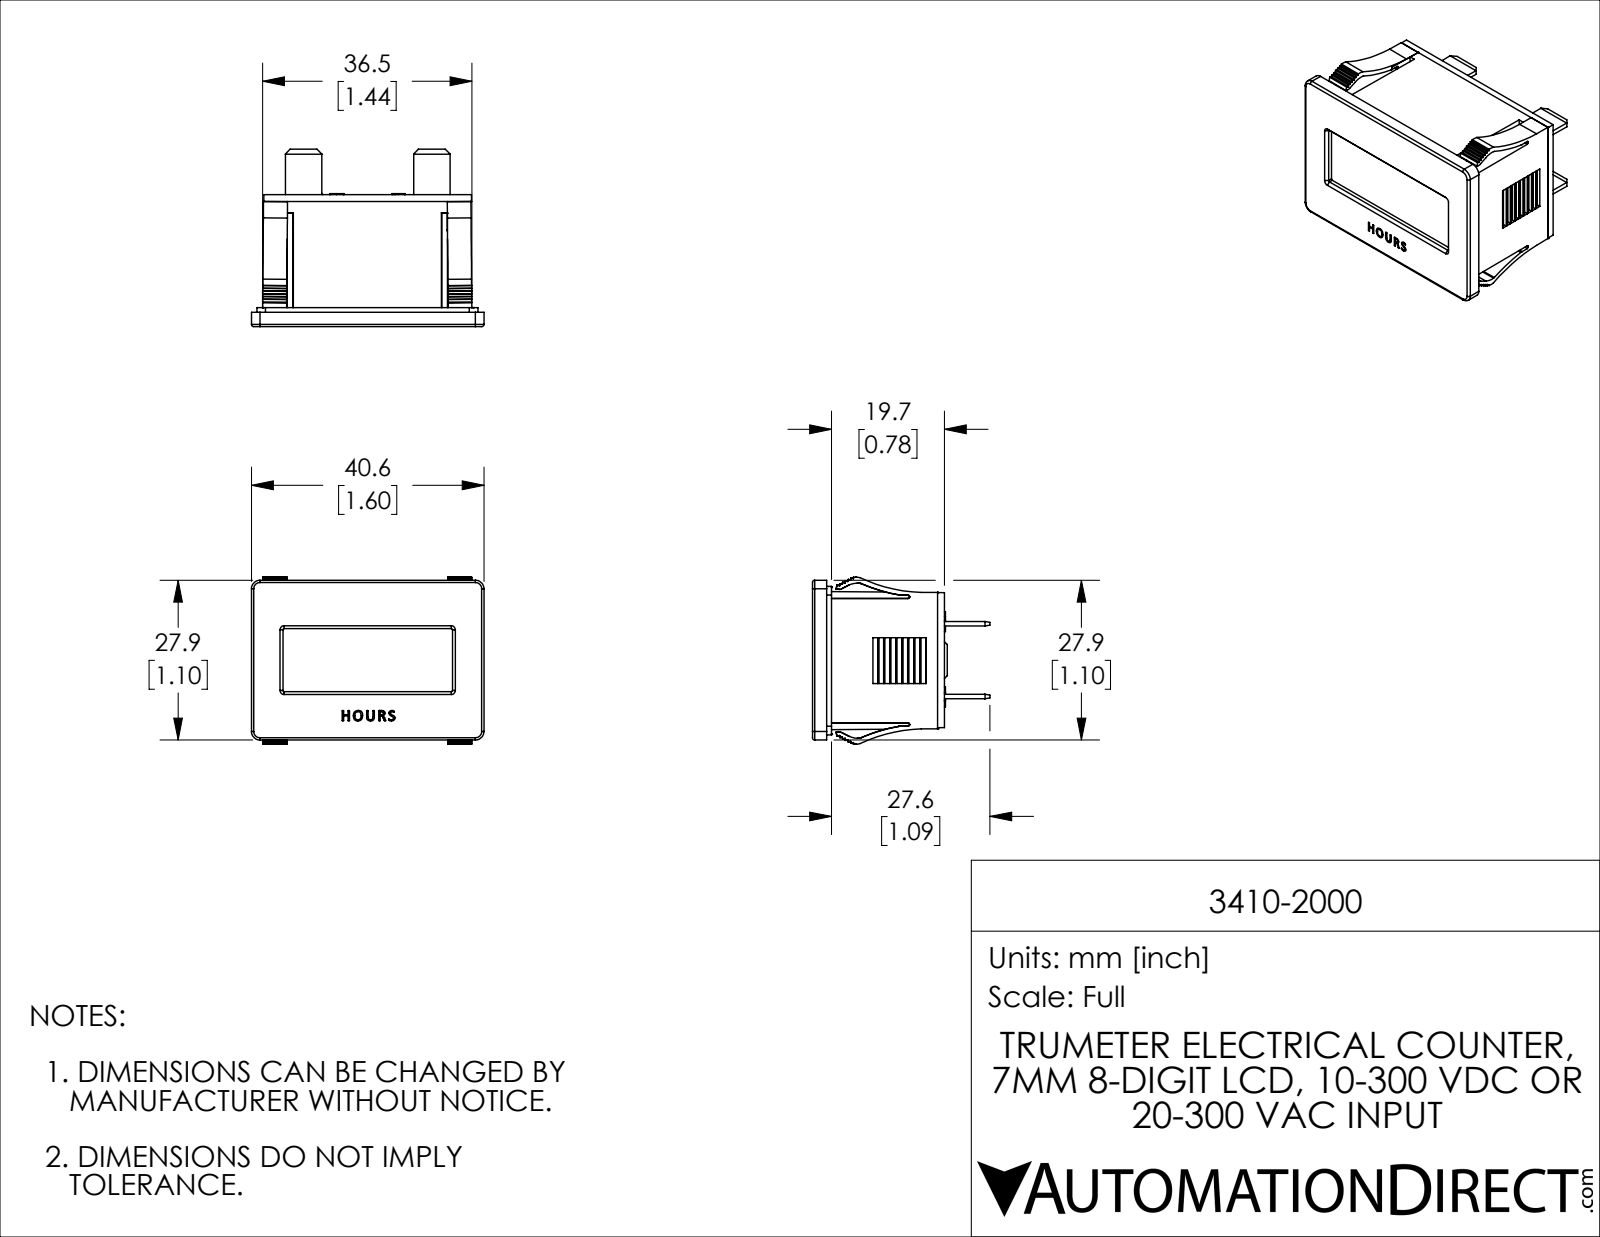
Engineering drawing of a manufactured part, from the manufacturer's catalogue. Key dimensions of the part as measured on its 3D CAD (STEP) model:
Part name (STEP PRODUCT): 3410-2000
STEP written by: SolidWorks 2021 (CONFIG_CONTROL_DESIGN)
Units: millimetres
Bodies: 1 solid, 722 faces (496 planar, 78 cylindrical, 148 other)
Overall size (bounding box): 40.6 × 30.98 × 29.16
Volume: 20 225 mm³ · Surface area: 7 847 mm²
Partial cylindrical surfaces — rounded edges, fillets, slot ends (radius × count): R1.5 ×8, R0.25 ×6, R0.2 ×4, R0.4 ×4, R0.76 ×4, R0.14 ×2, R0.25 ×2, R0.37 ×2
Main face-to-face distances: 1.2, 21.84, 23.04, 1.23, 21.81, 0.8, 20.61, 20.64, 12.7, 21.04
